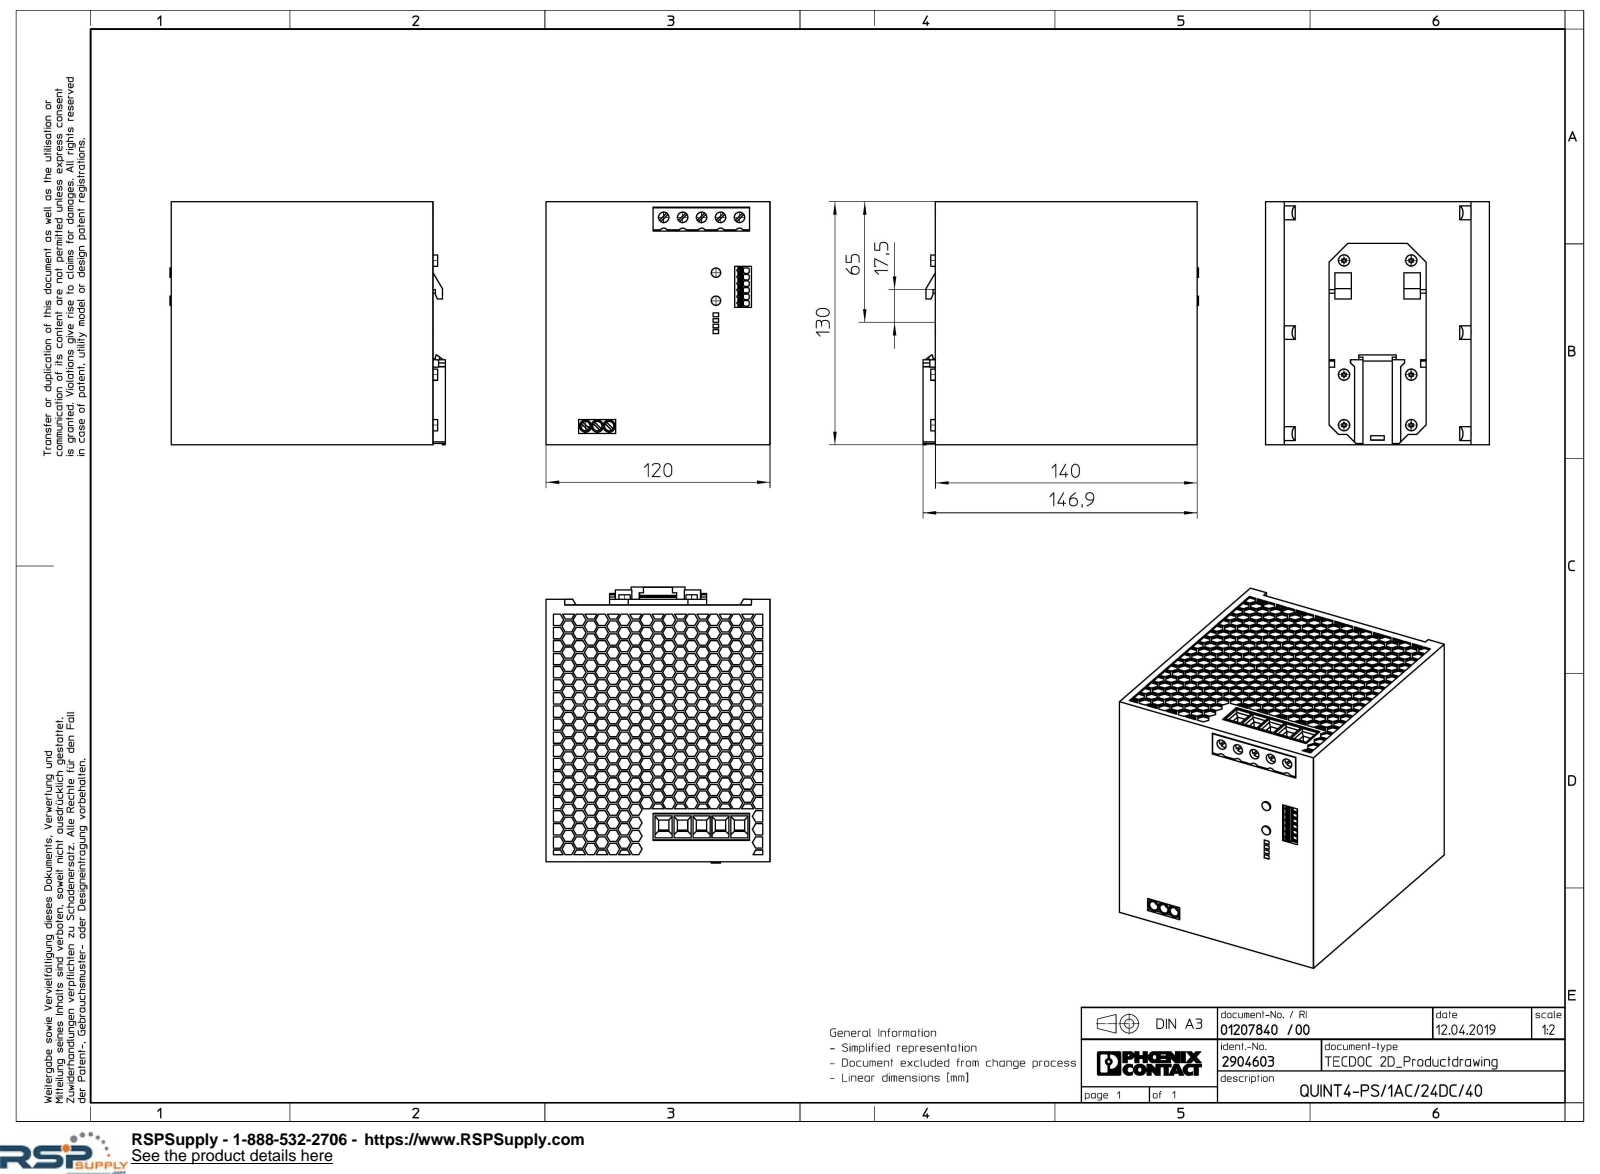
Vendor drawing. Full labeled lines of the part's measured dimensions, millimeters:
Part name (STEP PRODUCT): QUINT4_PS_1AC_24DC_40-select
STEP written by: Creo Elements/Direct Modeling 20.1A 29-Sep-2018 (C) Parametric Technology GmbH (AUTOMOTIVE_DESIGN)
Units: millimetres
Bodies: 1 solid, 5283 faces (5124 planar, 147 cylindrical, 12 other)
Overall size (bounding box): 147.55 × 130 × 120
Volume: 2 152 000 mm³ · Surface area: 121 659 mm²
Round holes (diameter × count): ⌀5.6 ×5, ⌀5 ×3, ⌀6.11 ×1
Round bosses / shafts (diameter × count): ⌀6 ×6, ⌀5 ×2
Partial cylindrical surfaces — rounded edges, fillets, slot ends (radius × count): R0.1 ×72, R0.97 ×12, R0.57 ×6, R0.6 ×6, R2.3 ×5, R3.25 ×3, R3.75 ×2, R3.75 ×2
Main face-to-face distances: 120, 0.8, 129.2, 128.4, 137.25, 3, 140.25, 130, 6.5, 9.5
Hole centre spacings: 10.16, 20.32, 6.35, 30.48, 12.7, 40.64
